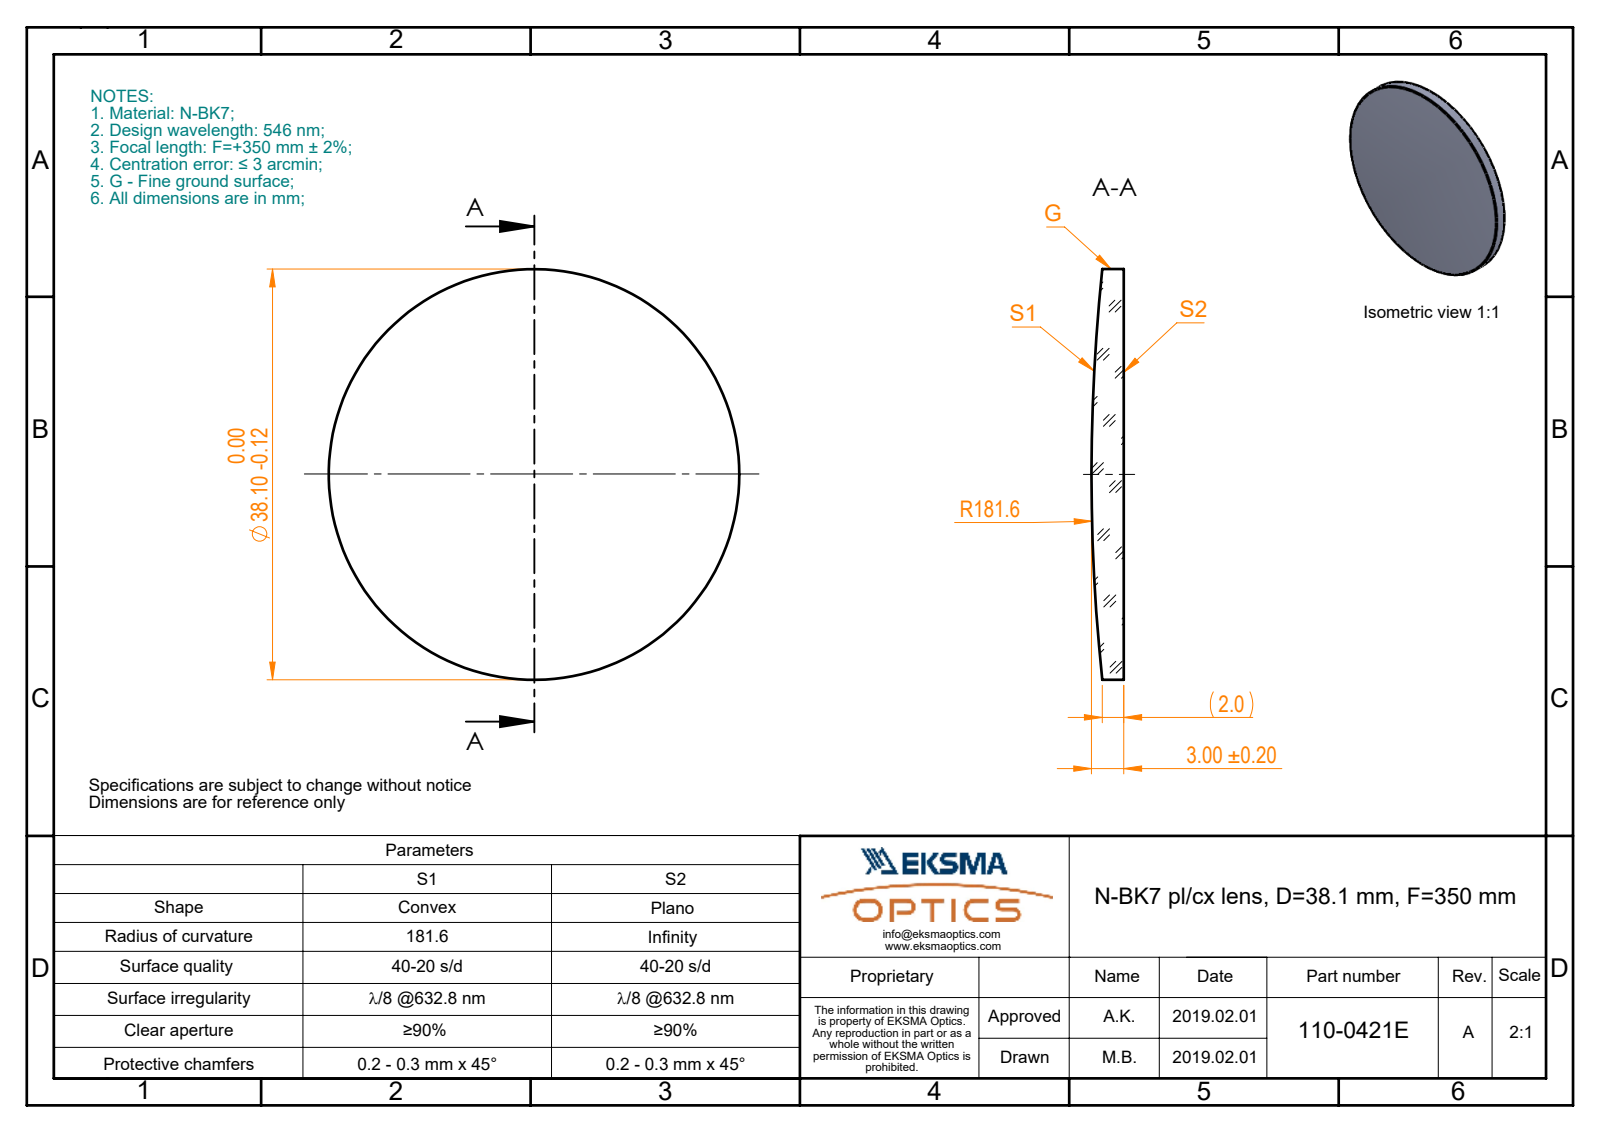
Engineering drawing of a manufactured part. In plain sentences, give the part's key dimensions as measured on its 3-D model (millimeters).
The part is named "110-0421E BK7 pl-cx 38.1 F350". Its 3-D file was written by "SolidWorks 2017 (CONFIG_CONTROL_DESIGN)". It is 1 solid with 5 faces: 1 planar, 2 cylindrical and 2 other. Overall it measures 38.1 by 38.1 by 3 millimeters. Its volume is 2 850 cubic millimeters and its surface area 2 522 square millimeters. Round bosses or shafts: 1 of diameter 38.1.
